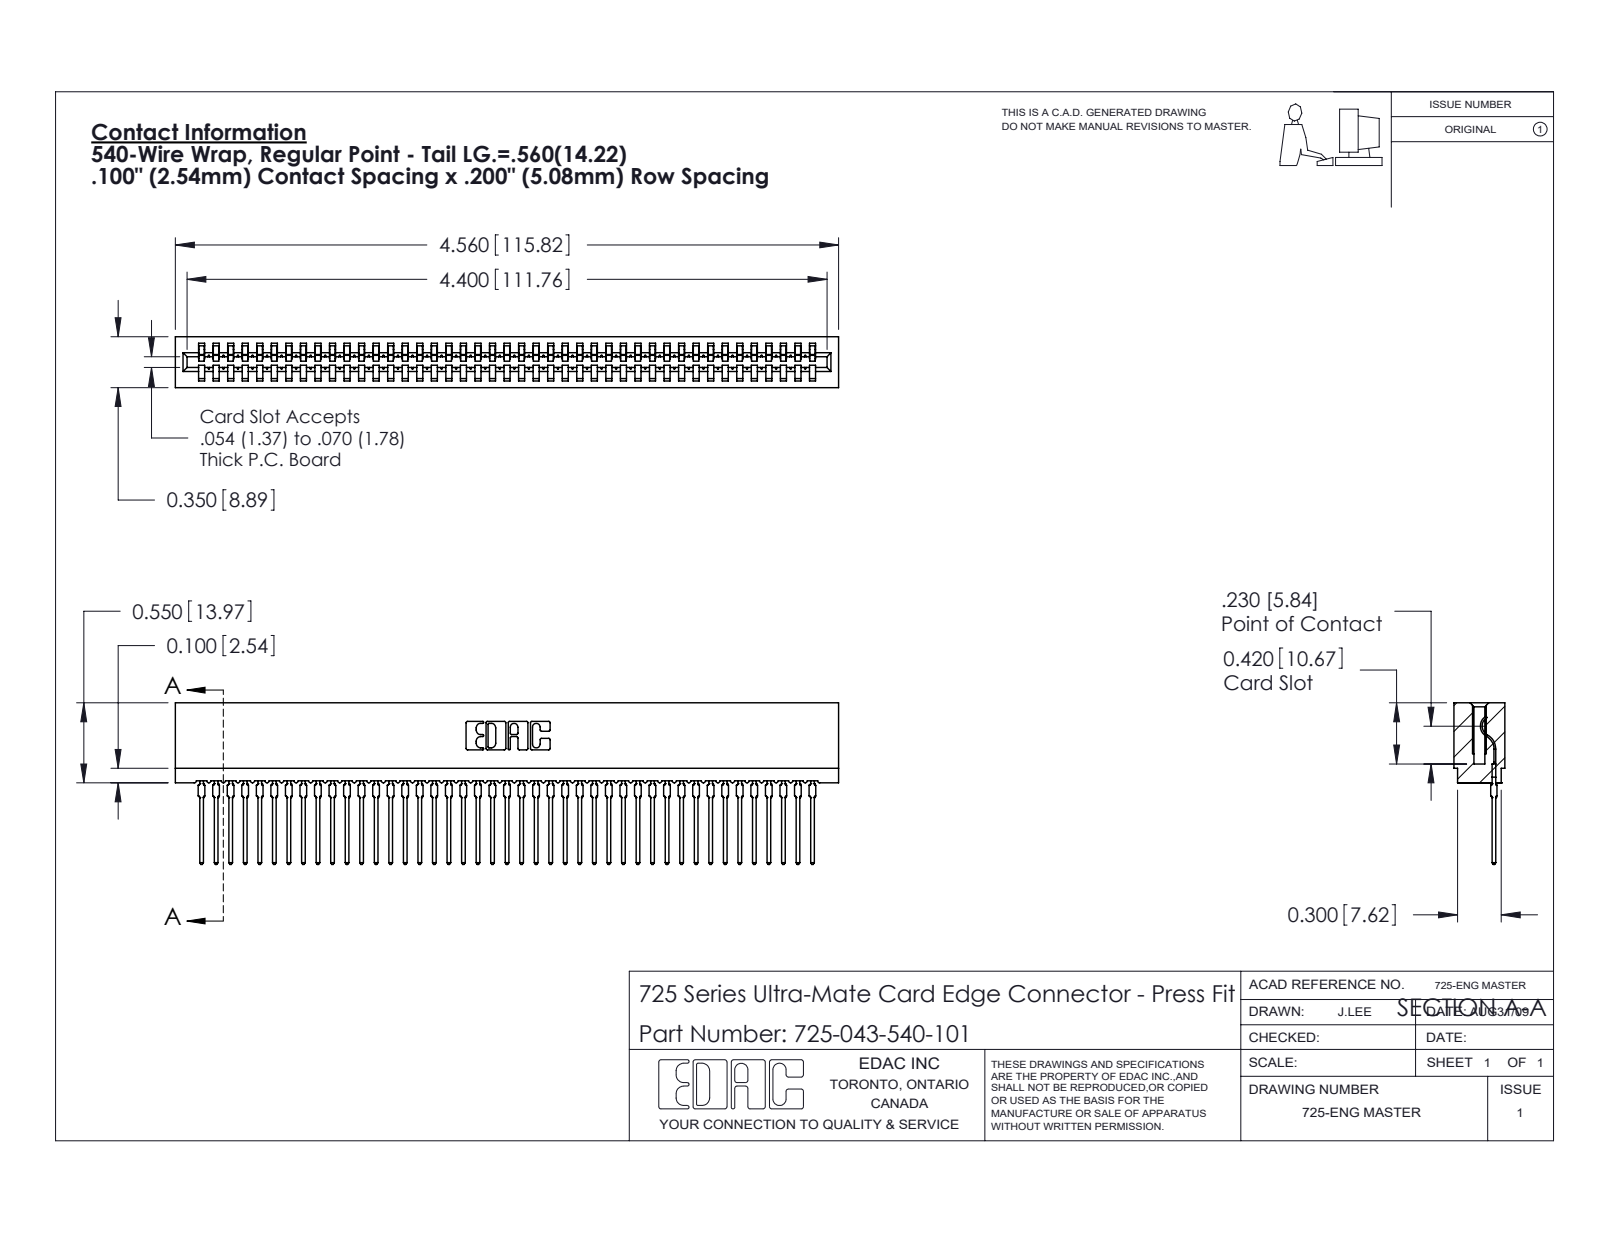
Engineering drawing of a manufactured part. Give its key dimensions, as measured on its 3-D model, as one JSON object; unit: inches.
{"part_name": "725-043-540-101; 725 Part_Insulator Option - 01; 745-292-001_540", "step_written_by": "SolidWorks 2020 (CONFIG_CONTROL_DESIGN)", "units": "inches", "bodies": {"solids": 44, "faces": 4911, "planar": 2936, "cylindrical": 857, "other": 1118}, "overall_size": [4.56, 1.111, 0.35], "volume_in3": 0.542, "surface_area_in2": 27.26, "partial_cylinders_radius": [[0.015, 86], [0.021, 86], [0.01, 22], [0.007, 6], [0.031, 6], [0.005, 4], [0.011, 4], [0.026, 3]], "face_to_face_distances": [0.35, 0.212, 0.138, 0.063, 0.287, 0.045, 0.305, 0.093, 0.167, 0.076]}
